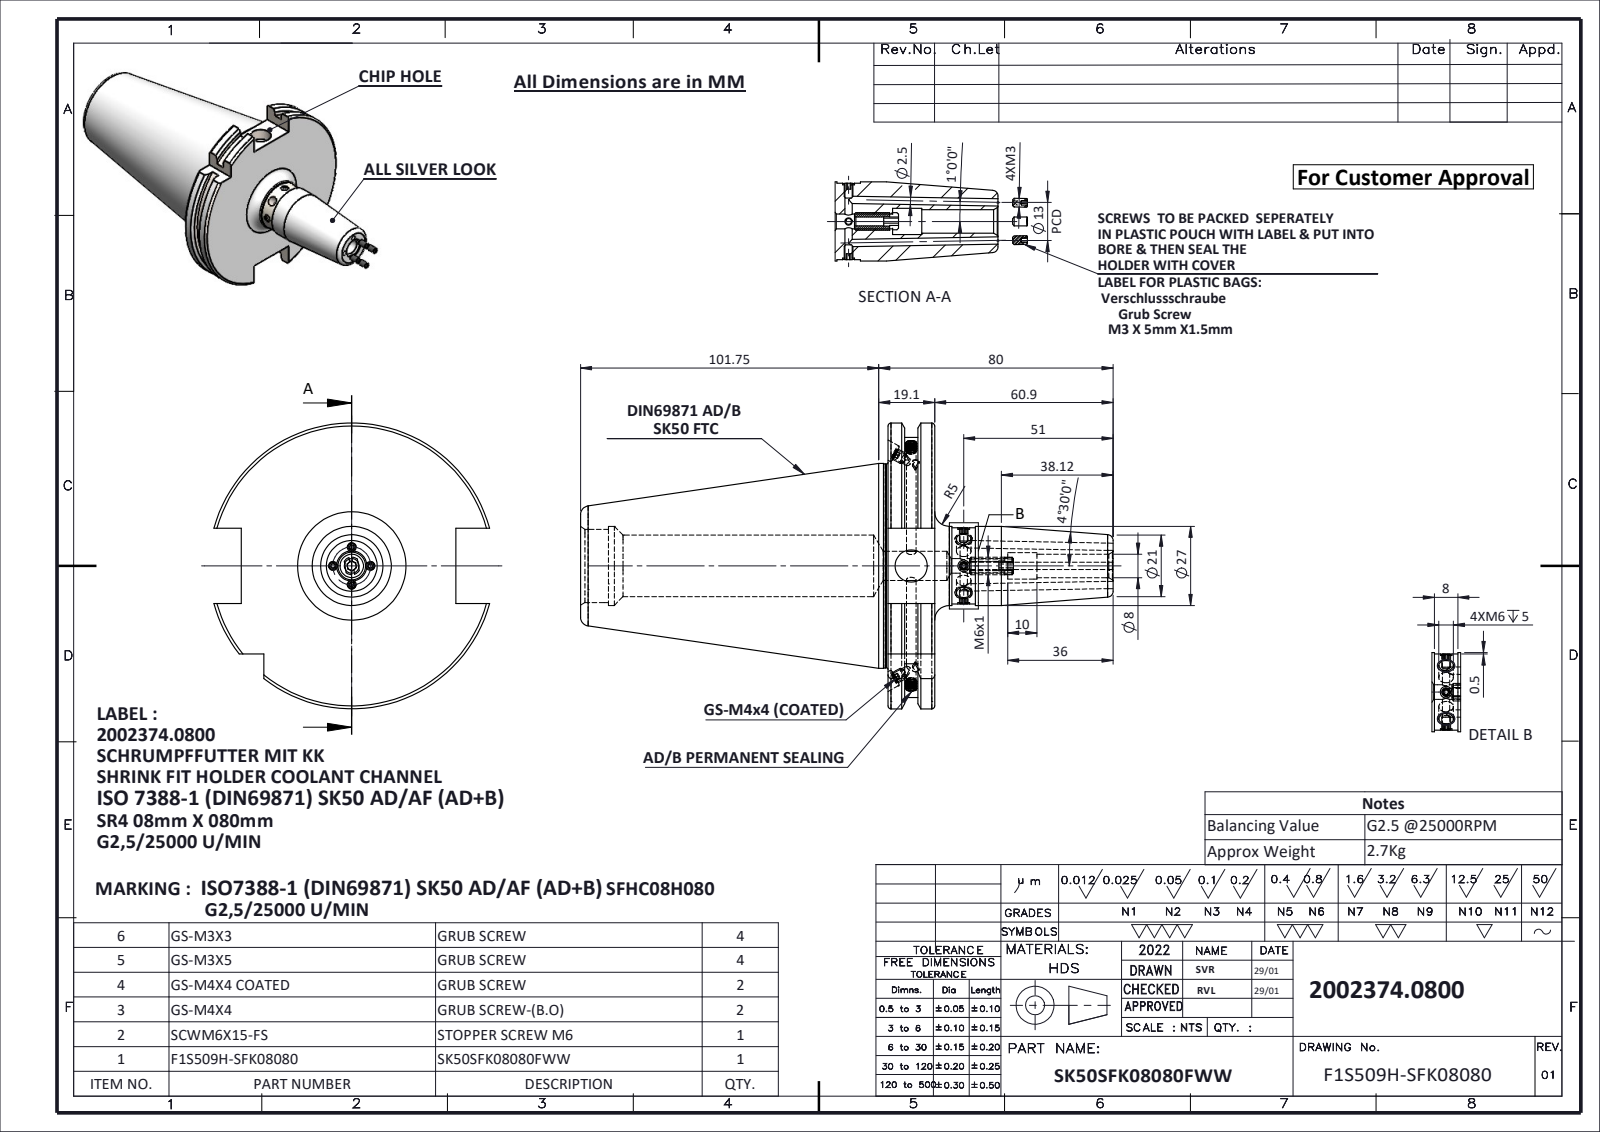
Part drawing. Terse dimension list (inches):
name: GS-M4X4-COATING_DIN 913 - M4 x 4-N; SCWM6x15-DOUBLE FLAT; socket set screw flat point_din_DIN 913 - M3 x 5-N; F1S509H-SFK08080 (+3 more)
written by: SolidWorks 2024 (CONFIG_CONTROL_DESIGN)
unit: in
bodies: 14 solids, 493 faces (188 planar, 141 cylindrical, 164 other)
size: 7.55 × 3.839 × 3.703
volume: 21.34 in³; area: 83.88 in²
holes: 6× ⌀0.098, 5× ⌀0.197, 2× ⌀0.126, 2× ⌀0.157, 2× ⌀0.236, 1× ⌀0.118, 1× ⌀0.13, 1× ⌀0.315, 1× ⌀0.354, 1× ⌀0.394, 1× ⌀0.433, 1× ⌀0.827
bosses: 6× ⌀0.118, 4× ⌀0.157, 2× ⌀0.114, 1× ⌀2.75, 1× ⌀2.734, 1× ⌀1.063, 1× ⌀1.024
rounds: 1× R0.118, 1× R1.768, 1× R1.919
face distances: 0.626, 0.223, 0.403, 0.399, 0.176, 0.227, 4.132, 4.355, 4.531, 4.758
hole spacings: 0.705
